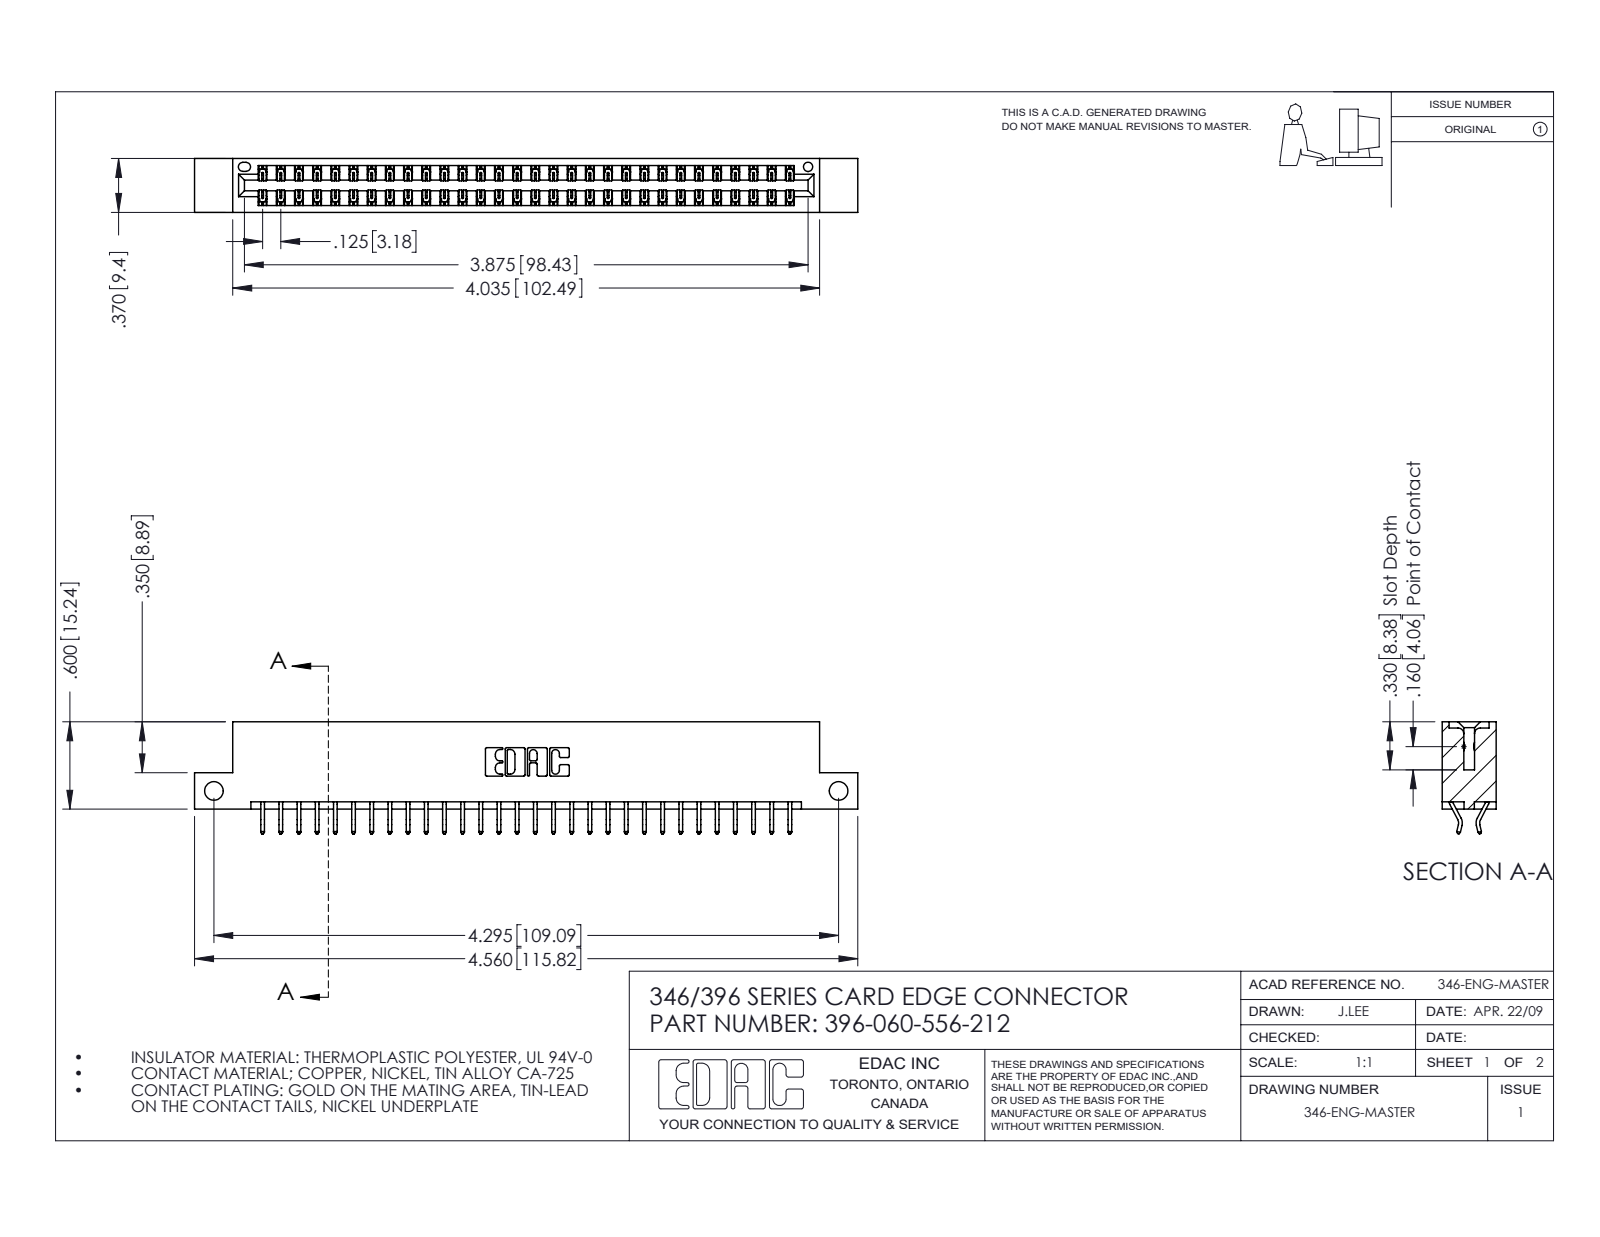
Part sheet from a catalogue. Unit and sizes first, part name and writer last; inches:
Units: inches
Overall size (bounding box): 4.56 × 0.77 × 0.37
Round holes (diameter × count): ⌀0.128 ×2, ⌀0.064 ×1
Partial cylindrical surfaces — rounded edges, fillets, slot ends (radius × count): R0.006 ×90, R0.01 ×22, R0.007 ×6, R0.031 ×6, R0.026 ×3, R0.01 ×2, R0.014 ×2, R0.022 ×2
Main face-to-face distances: 0.048, 0.322, 0.37, 0.25, 0.025, 0.072, 0.298, 0.275, 0.148, 0.222
Hole centre spacings: 4.295
Volume: 0.678 in³ · Surface area: 23.08 in²
Bodies: 61 solids, 3602 faces (2416 planar, 1186 cylindrical, 0 other)
Part name (STEP PRODUCT): 345-292-001_556 Tail; 396-060-556-212; 346 Part_Flush Mounting Lugs - Side Mount
STEP written by: SolidWorks 2016 (CONFIG_CONTROL_DESIGN)
